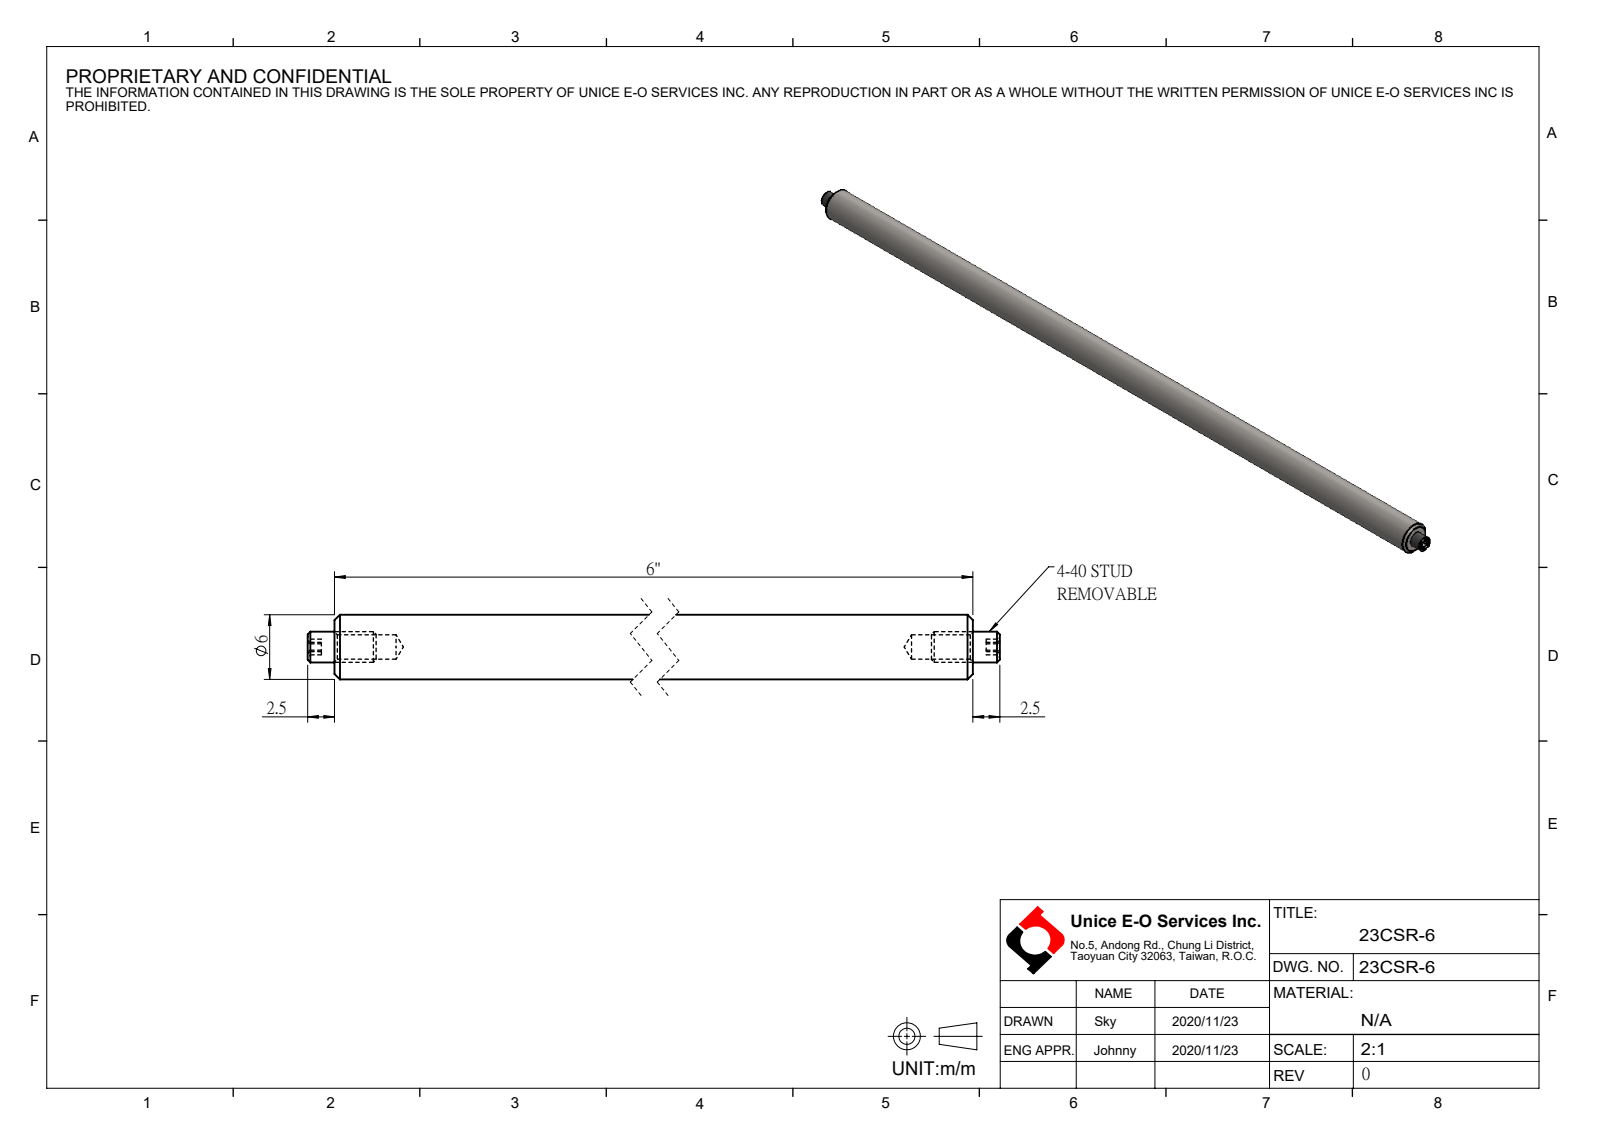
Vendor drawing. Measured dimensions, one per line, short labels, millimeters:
name: 23CSR-6
written by: SolidWorks 2016 (AUTOMOTIVE_DESIGN)
unit: mm
bodies: 0 solids, 42 faces (28 planar, 6 cylindrical, 8 other)
size: 157.4 × 6 × 6
bosses: 1× ⌀6, 1× ⌀2.84
face distances: 152.4, 1.27, 2.5, 154.9, 157.4
